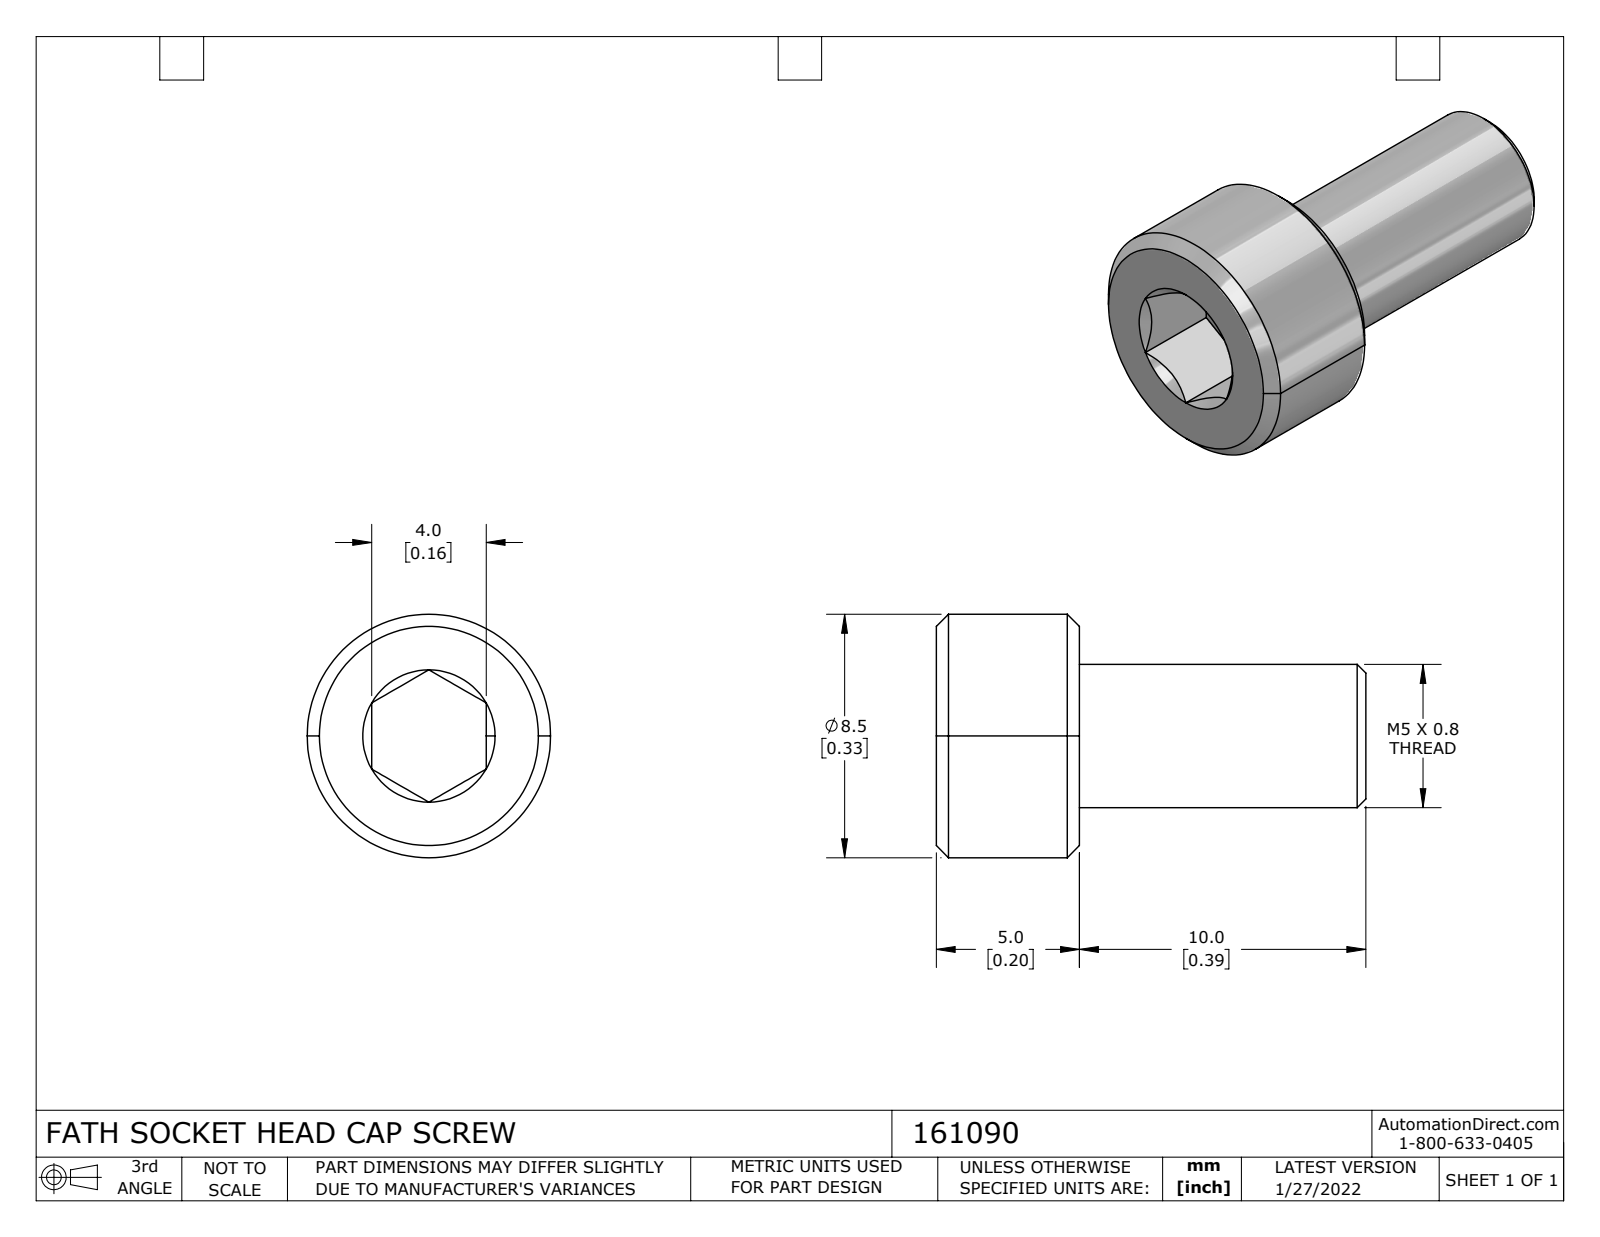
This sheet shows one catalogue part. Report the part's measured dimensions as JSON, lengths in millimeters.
{"part_name": "161090", "step_written_by": "SolidWorks 2021 (CONFIG_CONTROL_DESIGN)", "units": "millimeters", "bodies": {"solids": 1, "faces": 27, "planar": 10, "cylindrical": 4, "other": 13}, "overall_size": [15, 8.5, 8.5], "volume_mm3": 433, "surface_area_mm2": 427, "round_bosses_or_shafts": [[8.5, 1], [5, 1]], "face_to_face_distances": [5, 4, 15, 10, 3, 2, 12]}
